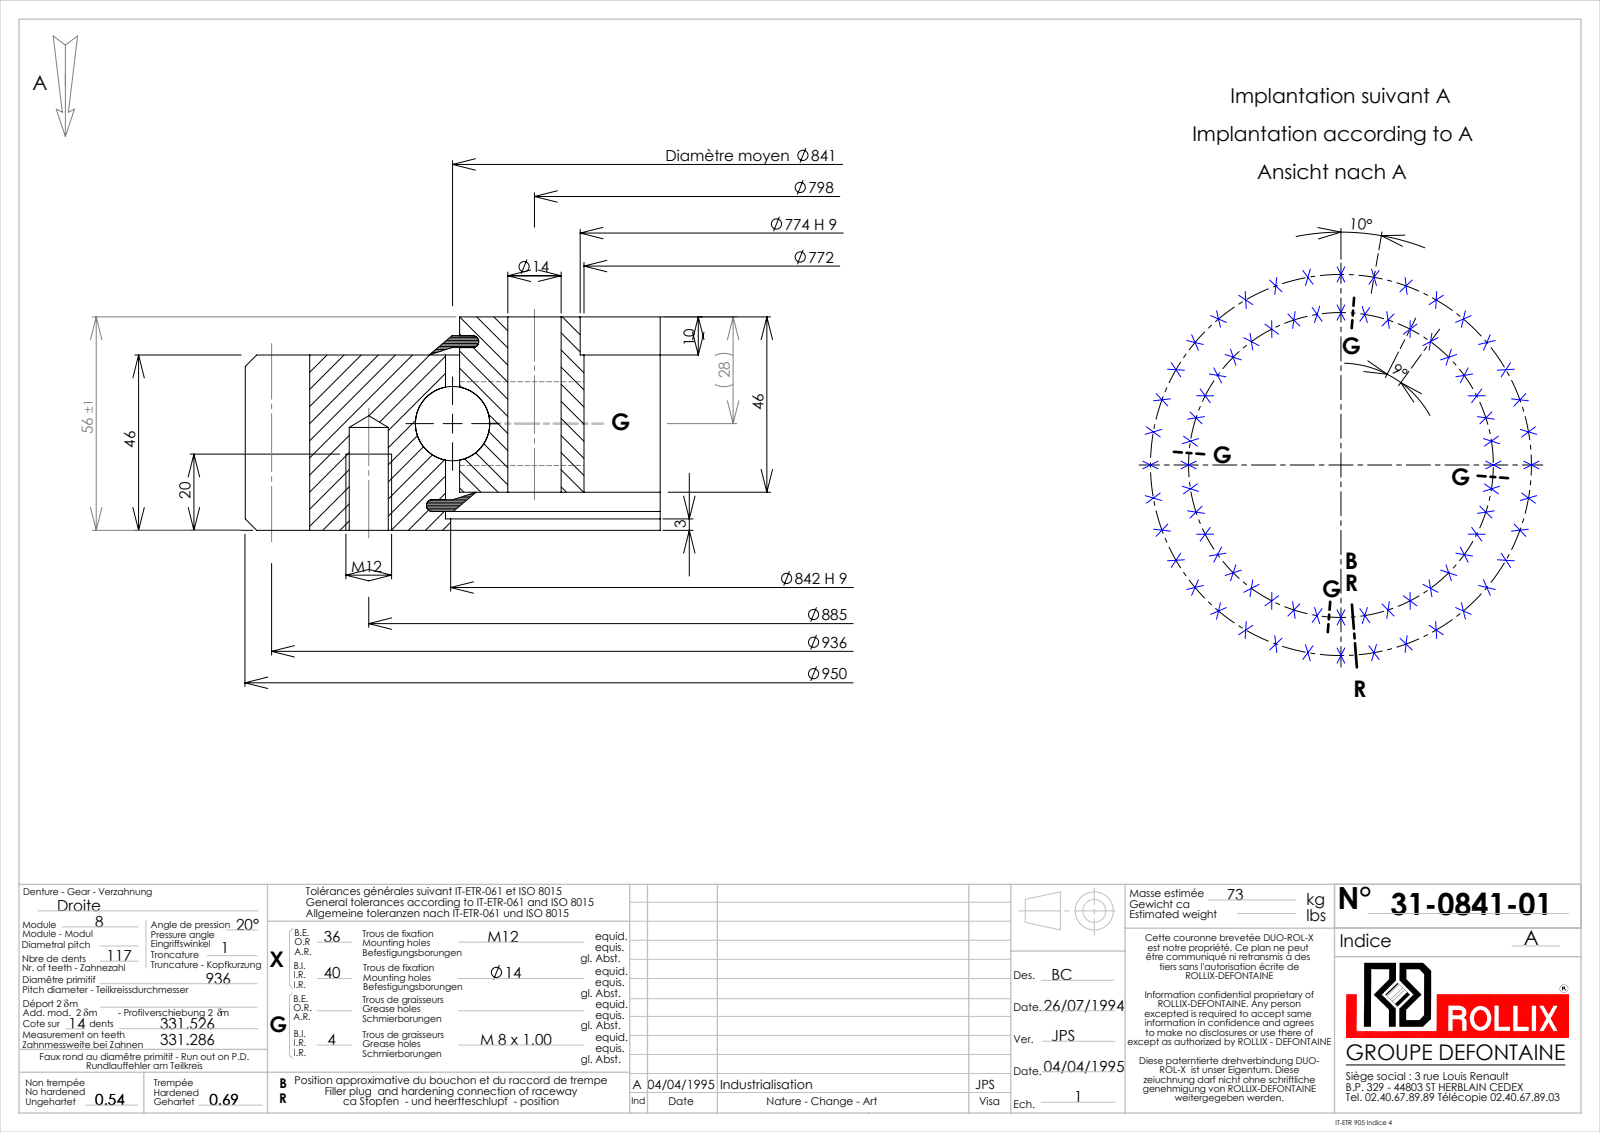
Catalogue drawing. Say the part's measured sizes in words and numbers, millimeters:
The part is named "31-0841-01". Its 3-D file was written by "SolidWorks 2016 (CONFIG_CONTROL_DESIGN)". It is 9 solids with 1088 faces: 405 planar, 307 cylindrical and 376 other. Overall it measures 949.99 by 949.92 by 56 millimeters. Its volume is 8 670 000 cubic millimeters and its surface area 1 388 000 square millimeters. Round holes: 40 of diameter 14, 36 of diameter 10.25, 4 of diameter 7, 1 of diameter 772, 1 of diameter 774, 1 of diameter 842, 1 of diameter 844.7, 1 of diameter 854.7. Round bosses or shafts: 4 of diameter 8, 1 of diameter 837.3, 1 of diameter 827.3. Partial cylindrical surfaces (rounded edges, fillets, slot ends): 1 of radius 475. The main face-to-face distances are 46, 10, 36, 56, 1.95, 5.05, 43, 4.95, 8.05, 47.95. The hole center spacings are 442.5, 77.13, 153.68, 229.05, 302.69, 677.95, 881.63, 442.49.
